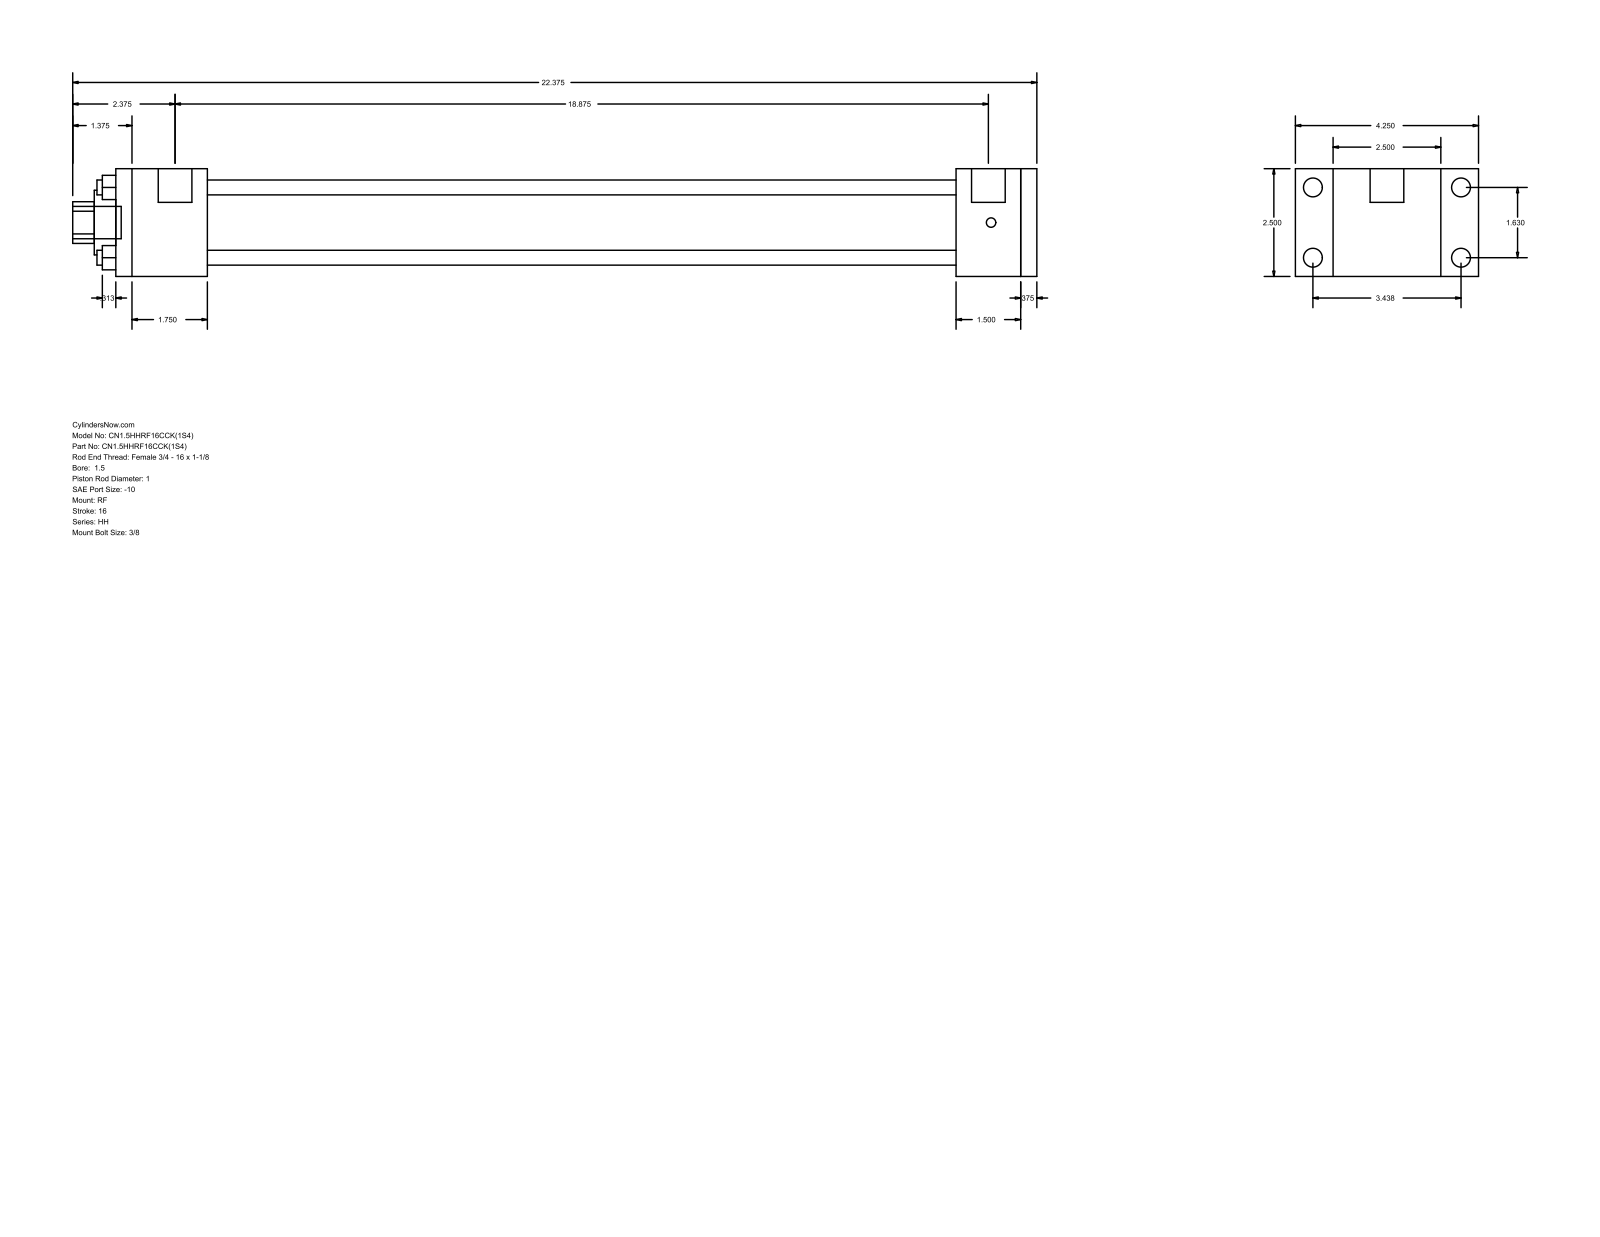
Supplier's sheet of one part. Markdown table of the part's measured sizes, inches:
| quantity | value |
| --- | --- |
| part name | HH_RF__0150_1 |
| STEP written by | GSSL Pune (CONFIG_CONTROL_DESIGN) |
| units | inches |
| bodies | 0 solids, 92 faces (64 planar, 28 cylindrical, 0 other) |
| overall size | 22.375 × 4.25 × 2.5 |
| round holes (diameter × count) | 0.345 × 4, 1 × 1, 1.5 × 1, 1.75 × 1 |
| round bosses / shafts (diameter × count) | 0.438 × 4, 0.219 × 4, 0.781 × 2, 0.75 × 1 |
| partial cylindrical surfaces (radius × count) | 0.484 × 1 |
| main face-to-face distances | 2.5, 0.375, 17.375, 18.875, 19.25, 1.5, 1.875, 2.125, 19.5, 21 |
| hole center spacings | 1.152, 1.63, 2.305 |
